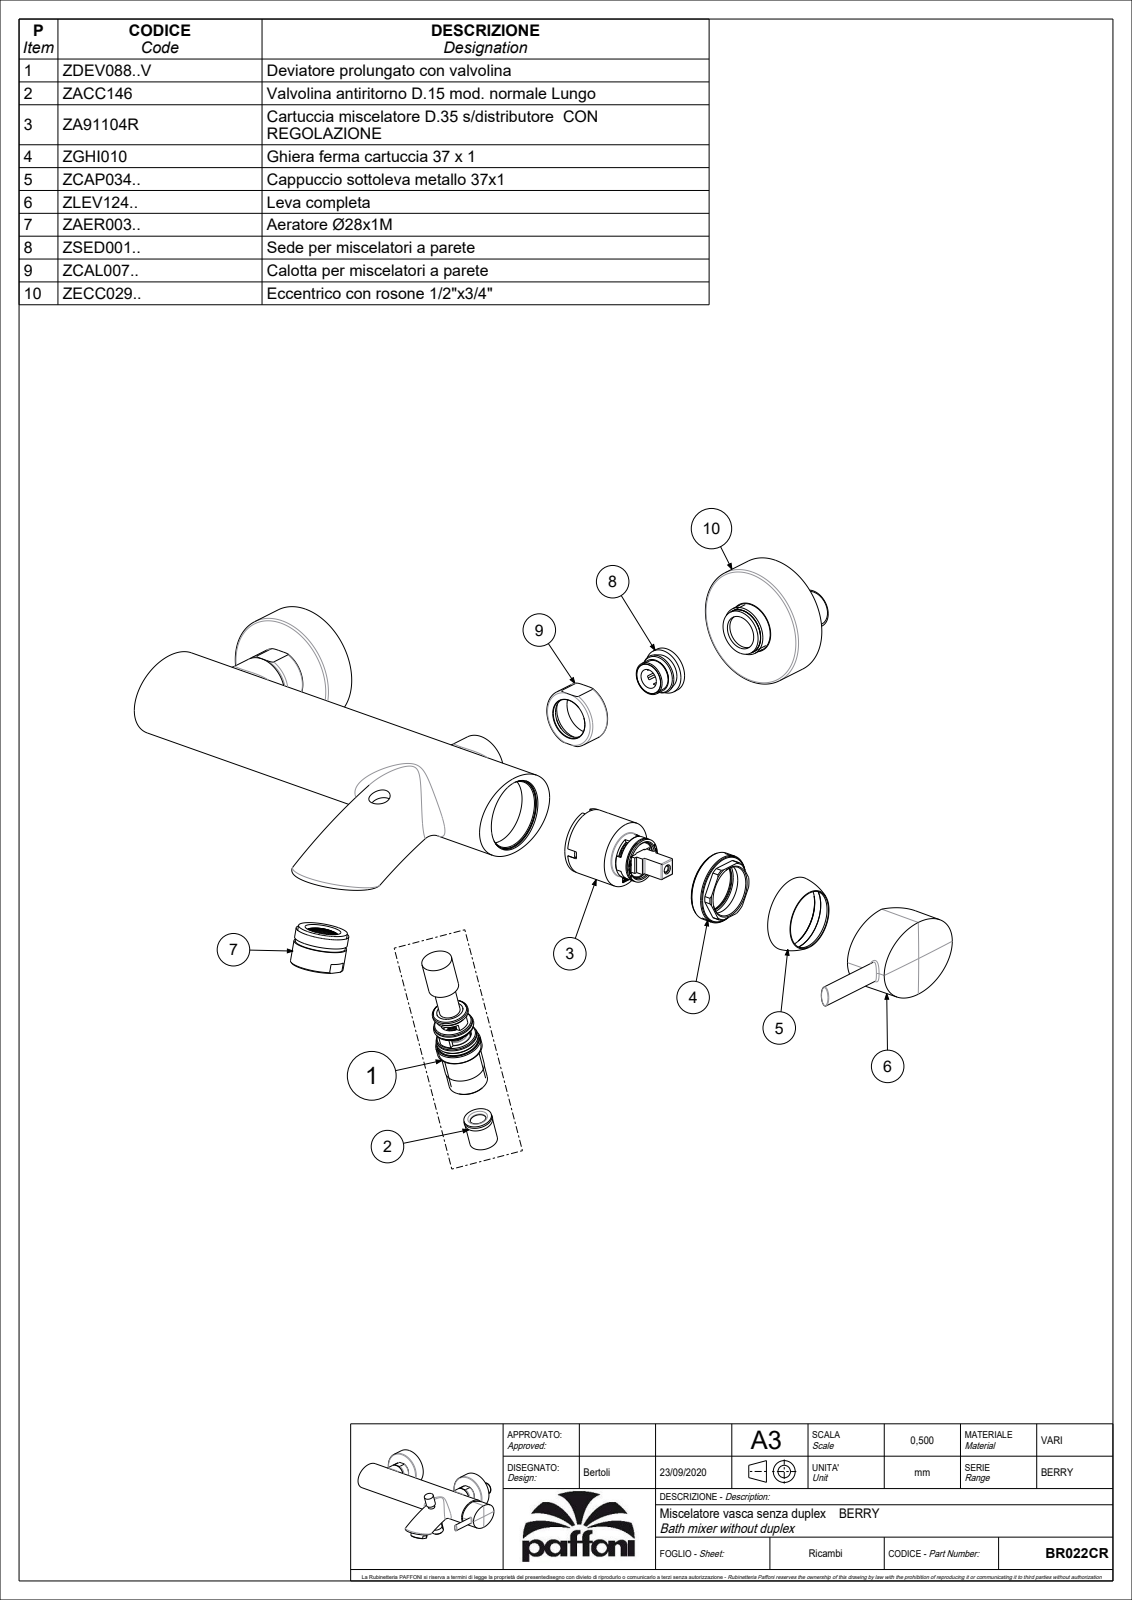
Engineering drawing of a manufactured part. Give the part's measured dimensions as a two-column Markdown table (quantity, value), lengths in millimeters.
| quantity | value |
| --- | --- |
| part name | BR022CR |
| STEP written by | CREO PARAMETRIC BY PTC INC, 2020044 (CONFIG_CONTROL_DESIGN) |
| units | millimeters |
| bodies | 3 solids, 2898 faces (2208 planar, 387 cylindrical, 303 other) |
| overall size | 263.55 × 177.7 × 80.39 |
| volume | 298 623 mm³ |
| surface area | 194 180 mm² |
| round holes (diameter × count) | 24.5 × 3, 25 × 3, 3.5 × 2, 4 × 2, 5 × 2, 7 × 2, 10.5 × 2, 16.7 × 2, 18 × 2, 21.6 × 2, 24.2 × 2, 27 × 2 |
| round bosses / shafts (diameter × count) | 24 × 3, 63.5 × 2, 31.2 × 2, 28 × 2, 27 × 2, 26.5 × 2, 35.5 × 1, 35 × 1 |
| partial cylindrical surfaces (radius × count) | 0.5 × 27, 0.15 × 11, 0.3 × 4, 1.25 × 4, 1 × 2, 4 × 1, 5.5 × 1, 6.5 × 1 |
| main face-to-face distances | 3.5, 39.5, 0.6, 38.9, 36, 35.4, 10, 8, 17, 3 |
| hole center spacings | 4.75, 7.63, 8.06, 8.2, 8.6, 9, 11.72, 12 |
